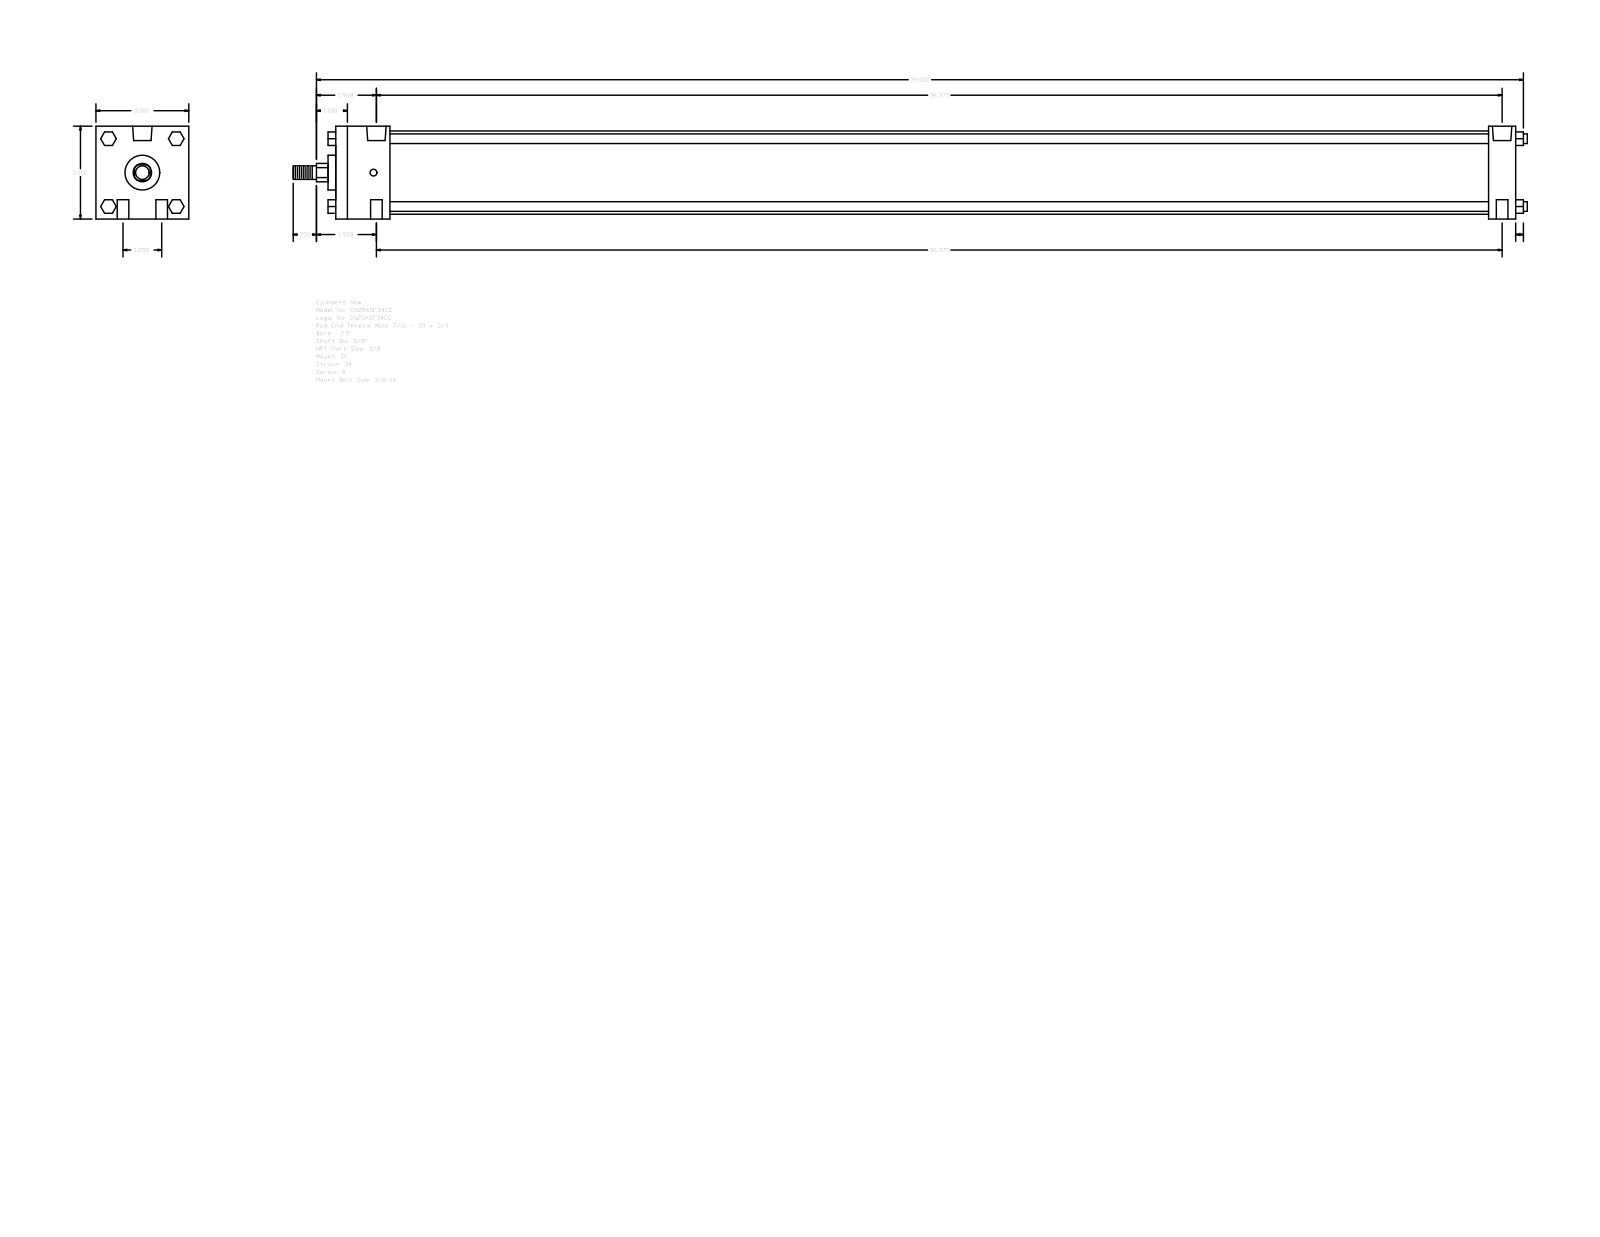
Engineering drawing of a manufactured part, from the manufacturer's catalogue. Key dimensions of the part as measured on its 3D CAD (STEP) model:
Part name (STEP PRODUCT): A_SF__0250_0.625
STEP written by: GSSL Pune (CONFIG_CONTROL_DESIGN)
Units: millimetres
Bodies: 0 solids, 124 faces (94 planar, 30 cylindrical, 0 other)
Overall size (bounding box): 1012.83 × 76.2 × 76.2
Round holes (diameter × count): ⌀9.53 ×4, ⌀5.56 ×2, ⌀15.93 ×2
Round bosses / shafts (diameter × count): ⌀7.94 ×4, ⌀68.33 ×1, ⌀28.57 ×1, ⌀15.88 ×1, ⌀11.11 ×1
Partial cylindrical surfaces — rounded edges, fillets, slot ends (radius × count): R7.54 ×1
Main face-to-face distances: 76.2, 968.37, 44.45, 946.14, 22.23, 901.69, 923.92, 6.35, 974.72, 50.8
Hole centre spacings: 15.88, 924.07, 923.93, 31.76, 924.48, 928.69
